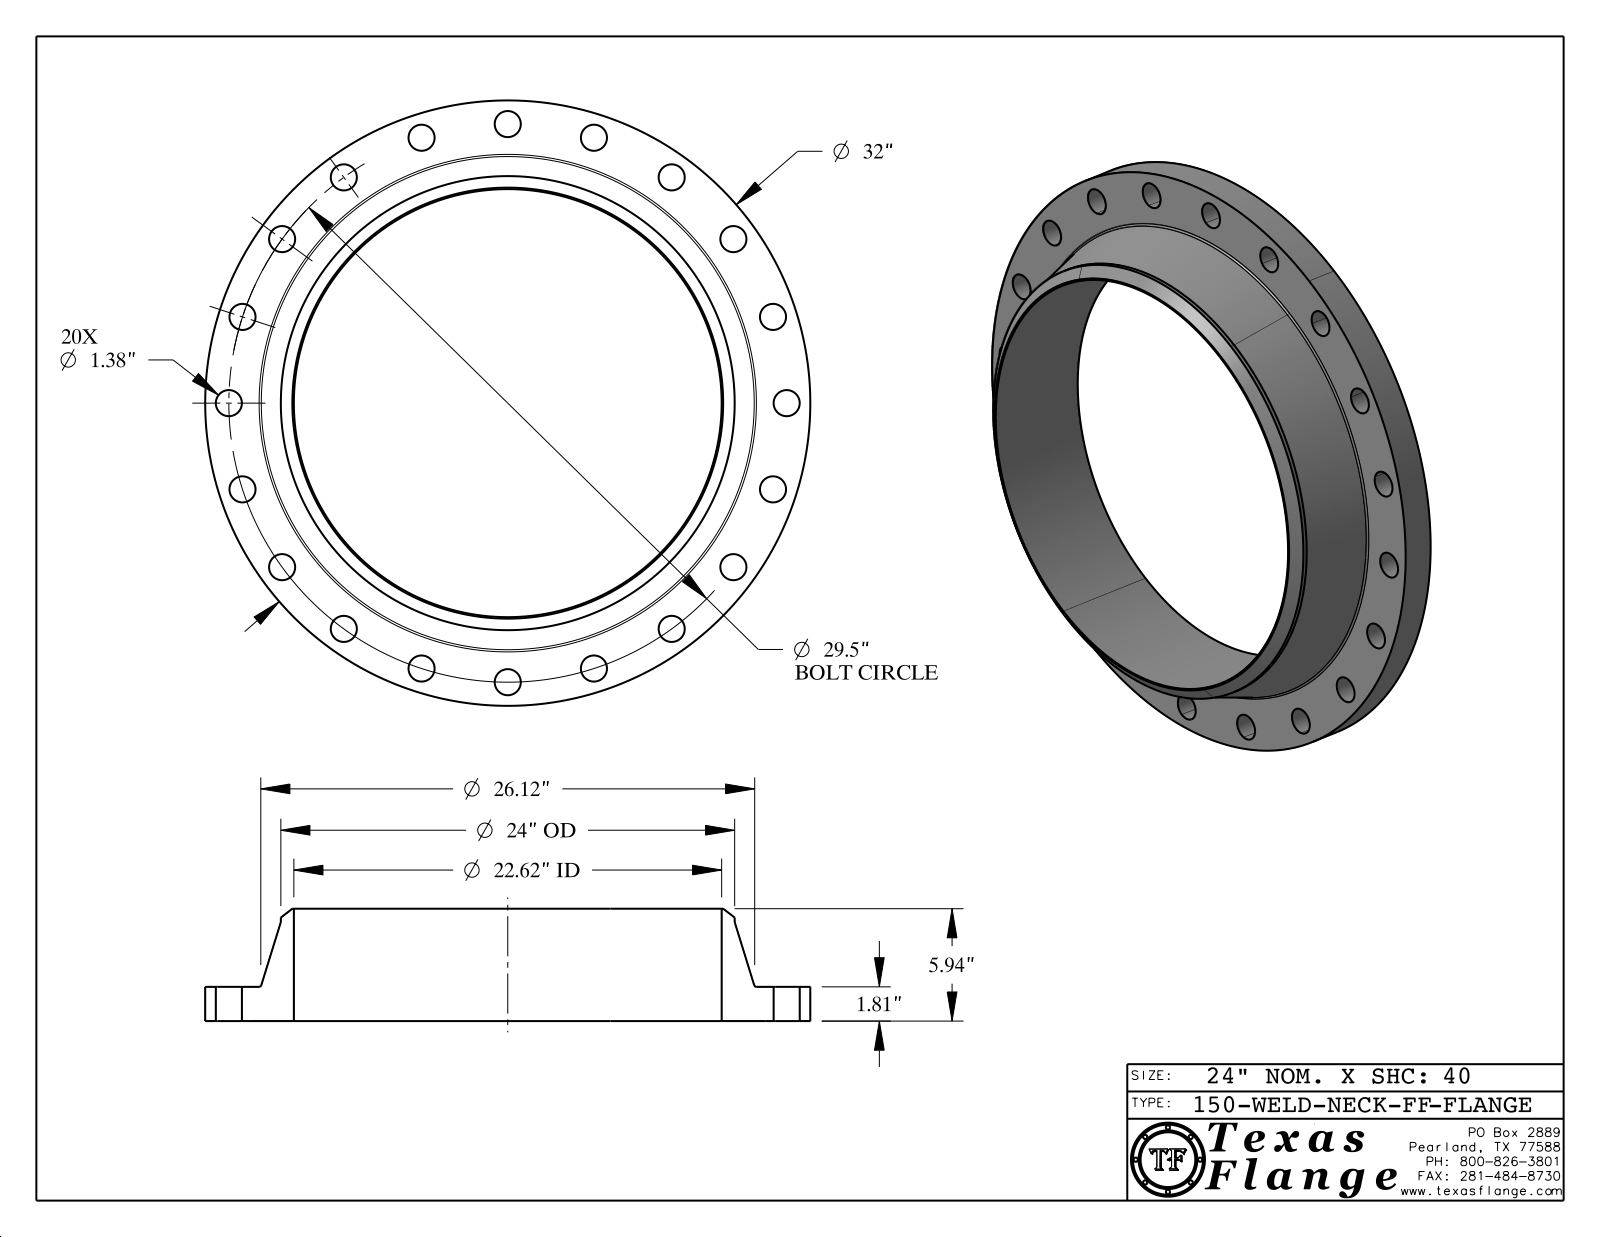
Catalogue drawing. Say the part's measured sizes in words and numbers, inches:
The part is named "150-WELD-NECK-FF". Its 3-D file was written by "CATIA V5 STEP AP214 (AUTOMOTIVE_DESIGN)". It is 1 solid with 441 faces: 369 planar, 66 cylindrical and 6 other. Overall it measures 32 by 32 by 5.94 inches. Its volume is 1 013 cubic inches and its surface area 1 732 square inches. Round holes: 20 of diameter 1.38, 1 of diameter 0.495, 1 of diameter 22.624. Round bosses or shafts: 8 of diameter 0.03, 1 of diameter 32, 1 of diameter 24, 1 of diameter 0.39. The main face-to-face distances are 1.81, 5.94, 4.13, 1.795, 0.015, 4.145, 0.148, 0.145, 0.027, 0.096. The hole center spacings are 14.75, 29.137, 4.615, 17.34, 20.859, 23.866, 26.285, 9.116.
